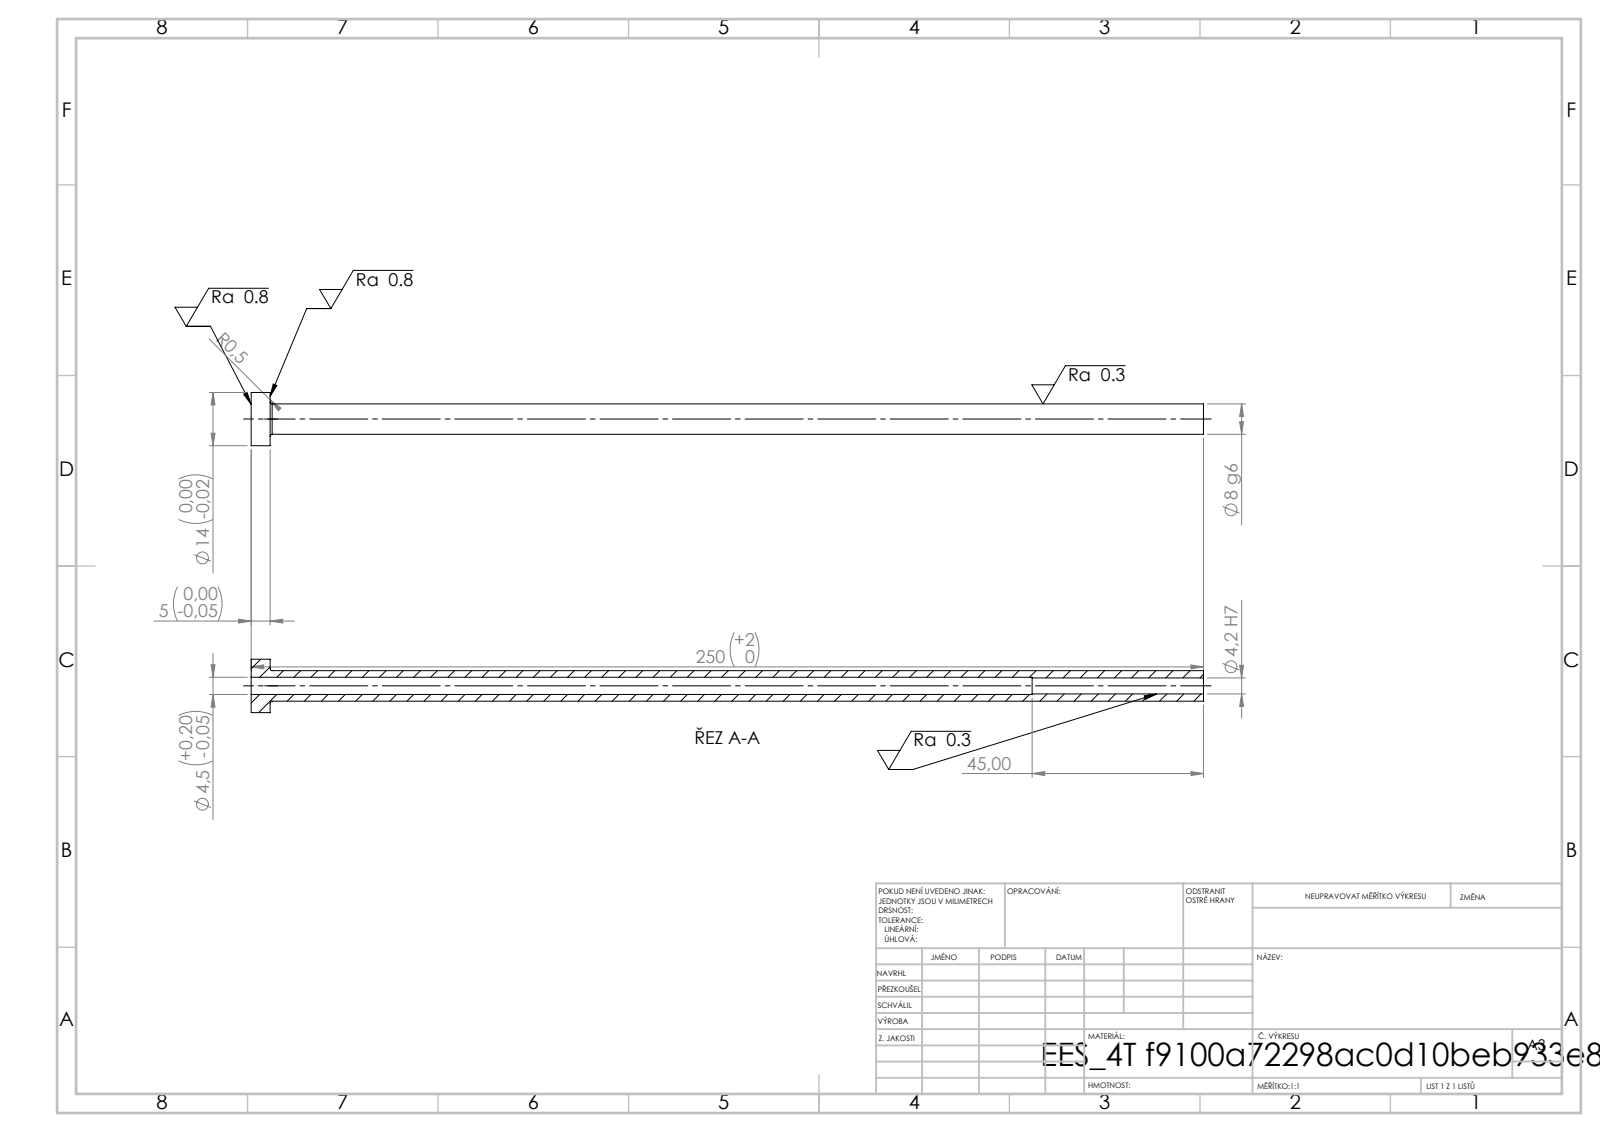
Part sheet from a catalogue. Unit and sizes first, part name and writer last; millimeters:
Units: millimetres
Overall size (bounding box): 250 × 14 × 14
Round holes (diameter × count): ⌀4.2 ×1, ⌀4.5 ×1
Round bosses / shafts (diameter × count): ⌀14 ×1, ⌀8 ×1
Main face-to-face distances: 5, 250, 245, 205, 200, 45
Volume: 9 202 mm³ · Surface area: 10 144 mm²
Bodies: 1 solid, 14 faces (4 planar, 8 cylindrical, 2 other)
STEP written by: SolidWorks 2019 (CONFIG_CONTROL_DESIGN)
